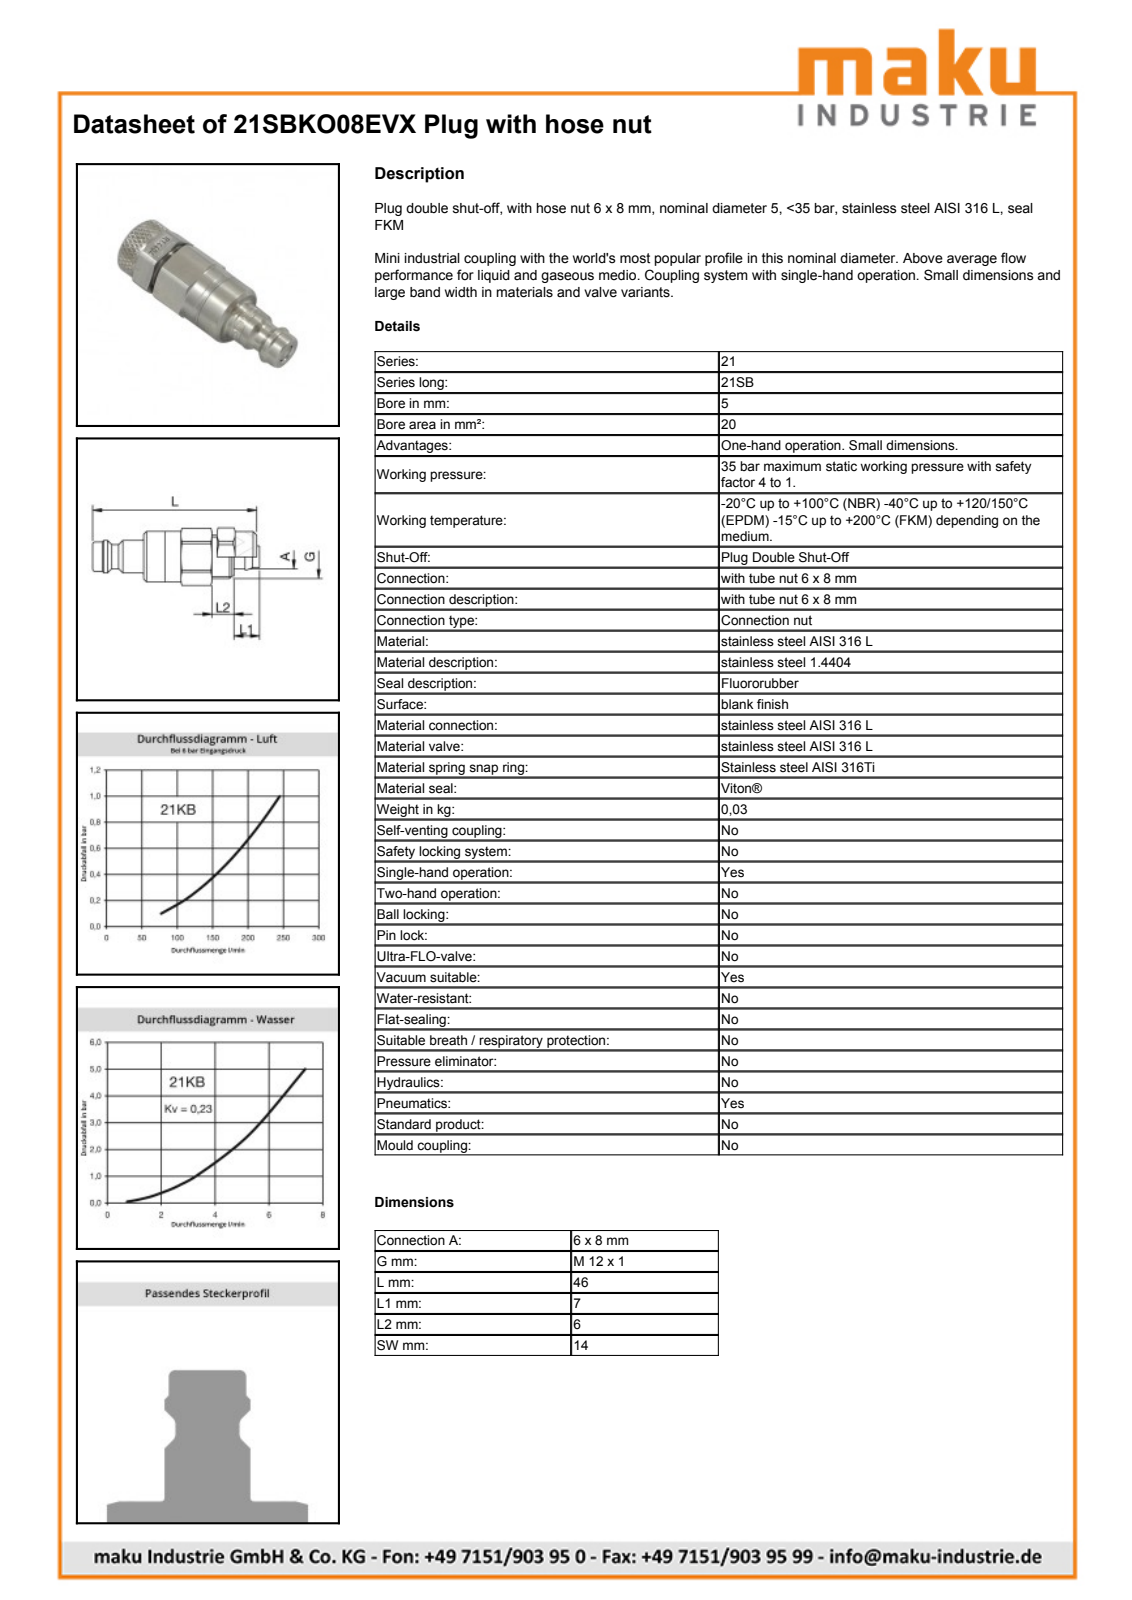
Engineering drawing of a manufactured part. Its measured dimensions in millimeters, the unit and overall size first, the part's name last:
Units: millimetres
Overall size (bounding box): 46 × 15.51 × 15.31
Round holes (diameter × count): ⌀11 ×1, ⌀12 ×1, ⌀12.1 ×1, ⌀12.5 ×1, ⌀12.6 ×1
Round bosses / shafts (diameter × count): ⌀14 ×1, ⌀10.85 ×1, ⌀10.79 ×1, ⌀10.4 ×1, ⌀9 ×1, ⌀8.1 ×1, ⌀6.7 ×1, ⌀6.05 ×1
Partial cylindrical surfaces — rounded edges, fillets, slot ends (radius × count): R7.75 ×1, R7.9 ×1
Main face-to-face distances: 14, 12.1, 1.1, 5, 6.1, 13.9, 6, 18.7, 24.8, 30.8
Volume: 5 174 mm³ · Surface area: 3 002 mm²
Bodies: 1 solid, 100 faces (23 planar, 29 cylindrical, 48 other)
Part name (STEP PRODUCT): D105924
STEP written by: Autodesk Inventor 2013 (AUTOMOTIVE_DESIGN)
